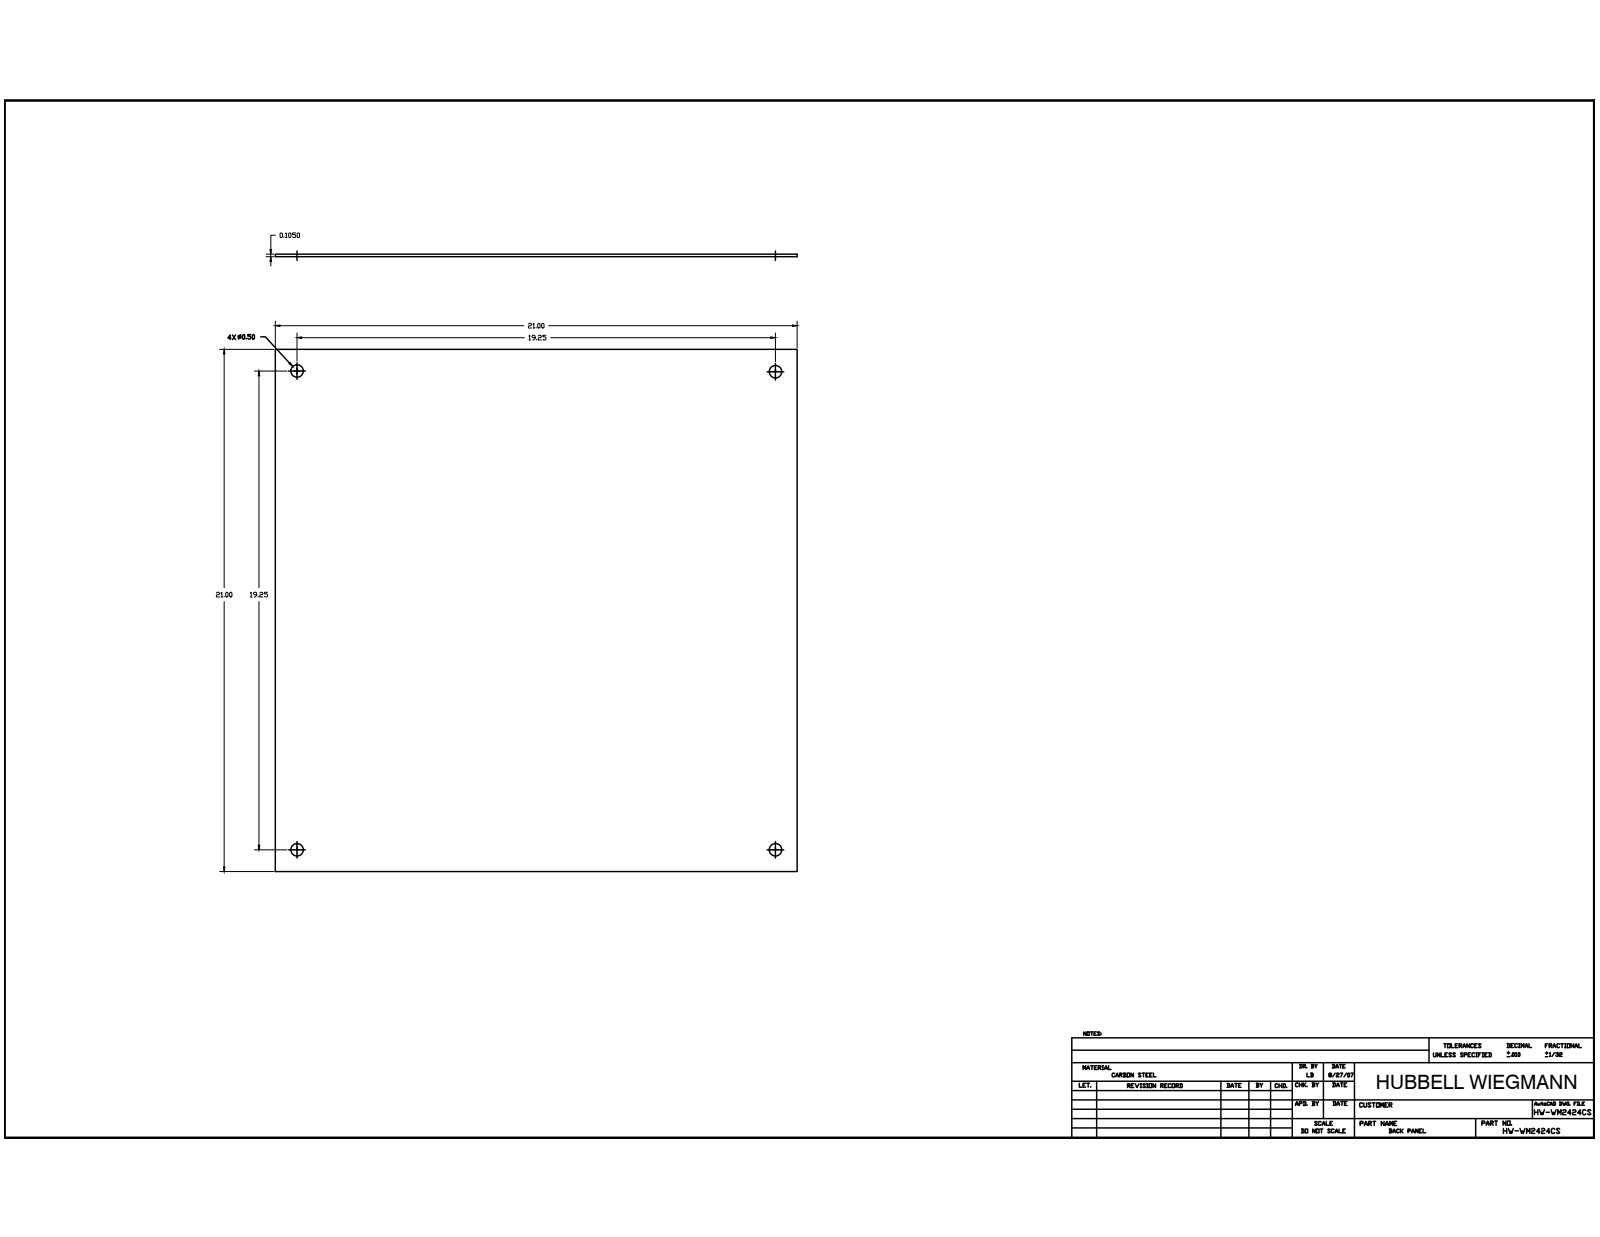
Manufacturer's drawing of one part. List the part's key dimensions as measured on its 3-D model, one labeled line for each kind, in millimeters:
Part name (STEP PRODUCT): BP2424CS_STP
STEP written by: Autodesk Inventor 2014 (CONFIG_CONTROL_DESIGN)
Units: millimetres
Bodies: 1 solid, 10 faces (6 planar, 4 cylindrical, 0 other)
Overall size (bounding box): 533.4 × 533.4 × 2.67
Volume: 757 452 mm³ · Surface area: 574 134 mm²
Round holes (diameter × count): ⌀12.7 ×4
Main face-to-face distances: 2.66, 533.4
Hole centre spacings: 488.94, 691.47
